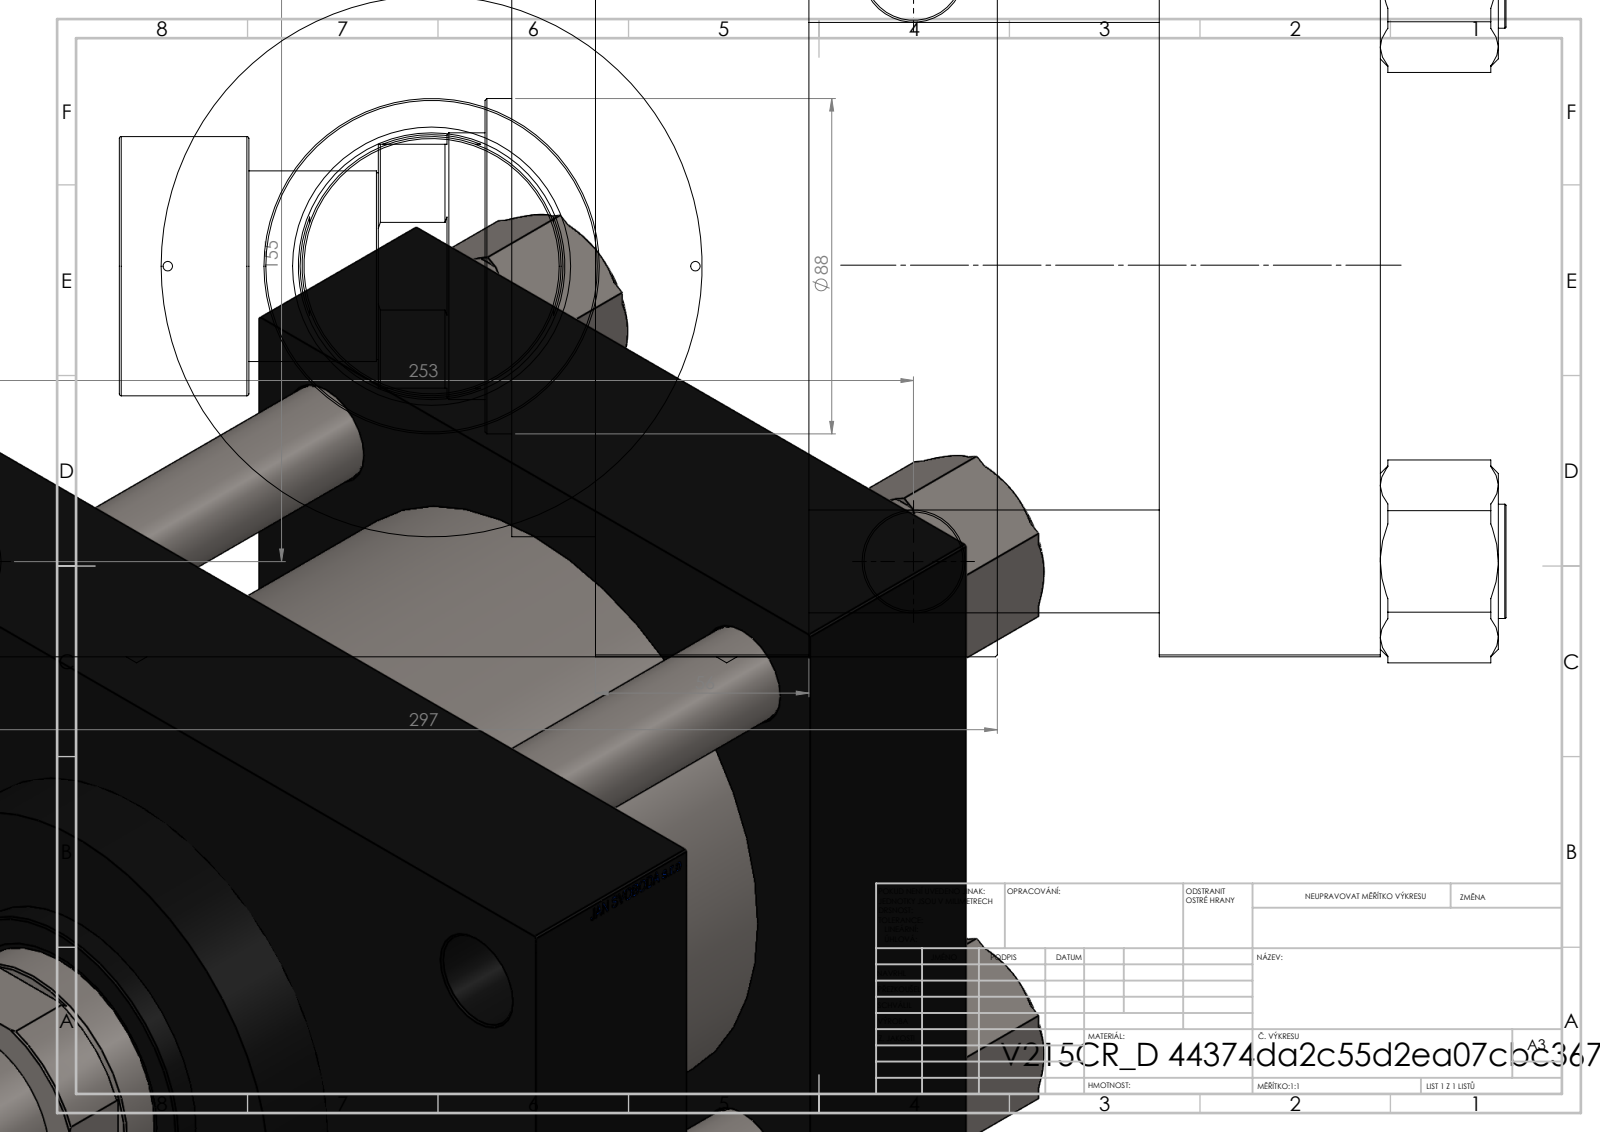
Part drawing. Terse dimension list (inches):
name: V215CR_ROD_END_F; V215CR_VCP_D; NUT_M5_D; V215CR_D_Body (+2 more)
written by: SolidWorks 2019 (CONFIG_CONTROL_DESIGN)
unit: in
bodies: 12 solids, 1168 faces (550 planar, 96 cylindrical, 522 other)
size: 14.331 × 11.693 × 8.194
volume: 491 in³; area: 1 162 in²
holes: 4× ⌀1.024, 4× ⌀1.063, 2× ⌀0.098, 2× ⌀0.276, 2× ⌀1.309, 2× ⌀1.772, 1× ⌀1.831, 1× ⌀2.756, 1× ⌀2.874, 1× ⌀4.724, 1× ⌀5.591, 1× ⌀6.299
bosses: 4× ⌀1.181, 1× ⌀6.535, 1× ⌀3.465, 1× ⌀2.677, 1× ⌀1.969, 1× ⌀1.929
face distances: 2.283, 5.906, 3.622, 8.11, 5.827, 2.205, 8.071, 1.811, 9.882, 2.835
hole spacings: 1.931, 3.066, 3.793, 4.312, 5.841, 6.098, 6.399, 6.531
